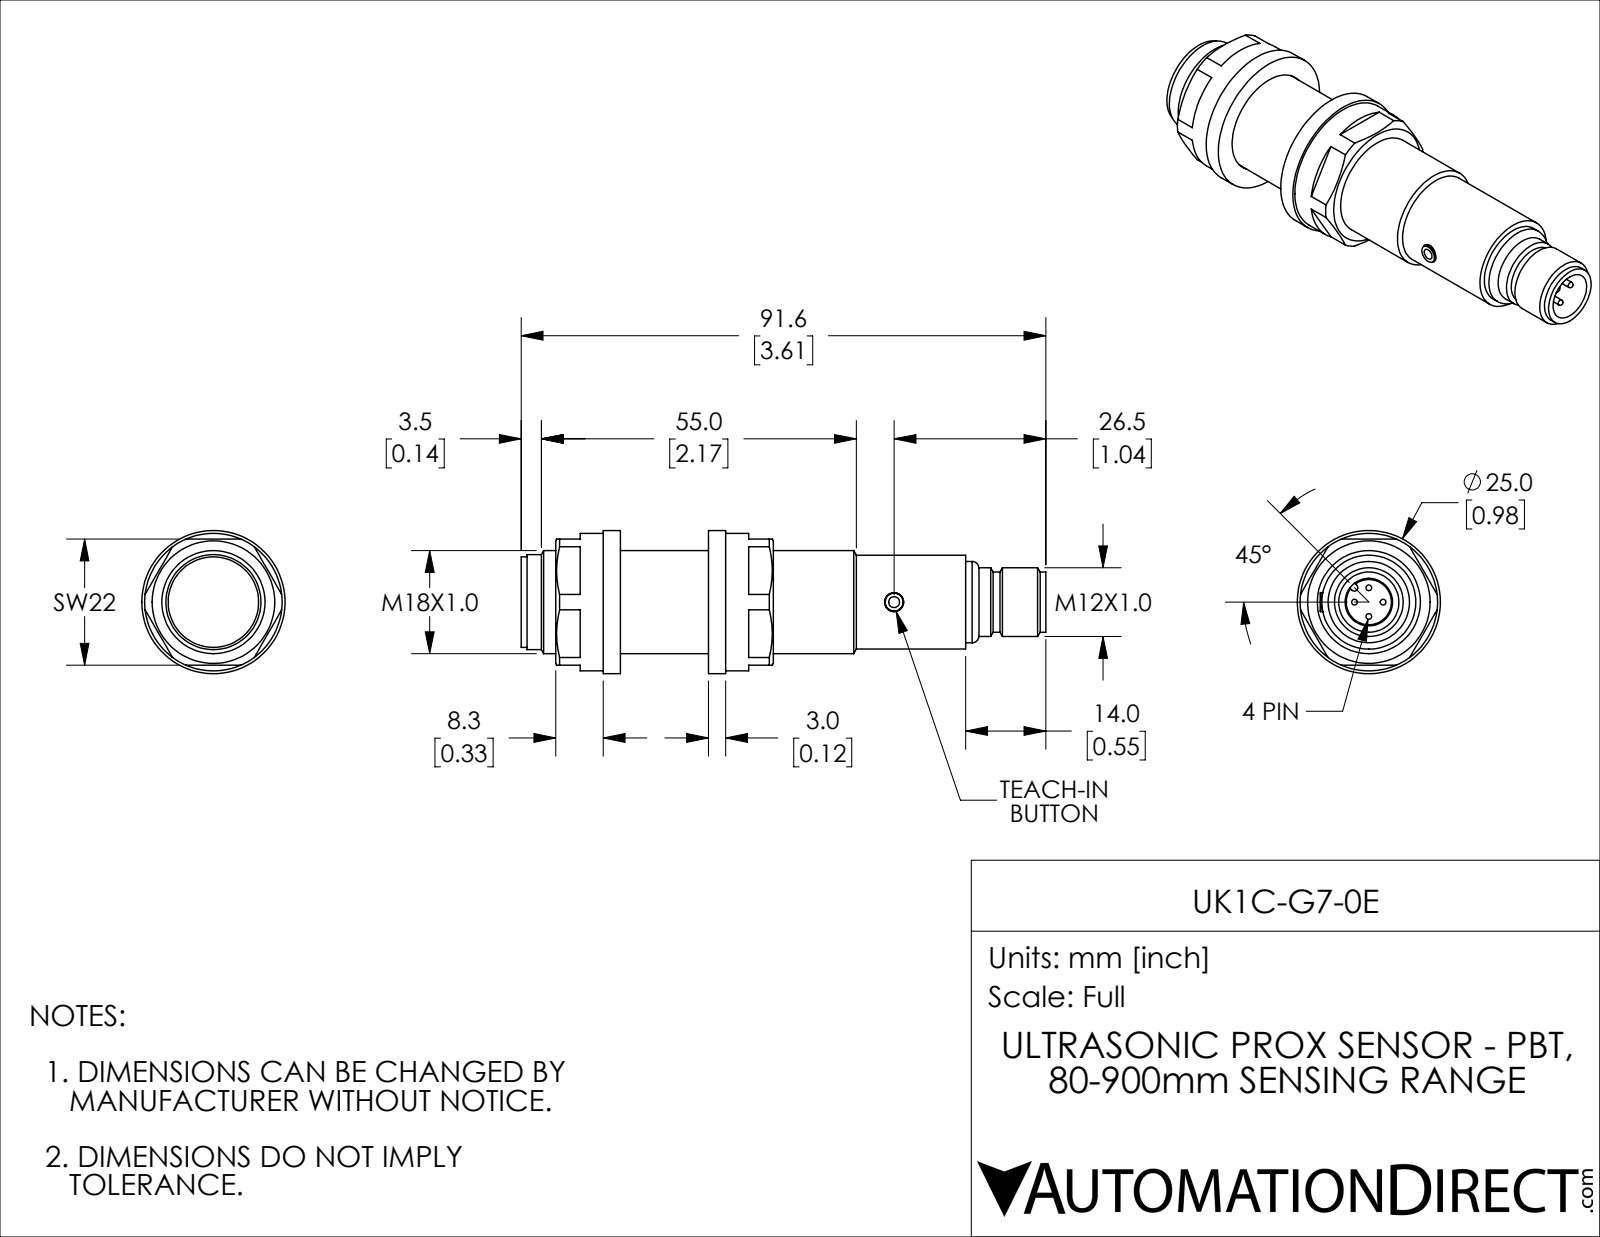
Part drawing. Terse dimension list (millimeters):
name: UK1C-G7-0E
written by: SolidWorks 2018 (AUTOMOTIVE_DESIGN)
unit: mm
bodies: 6 solids, 123 faces (43 planar, 49 cylindrical, 31 other)
size: 91.6 × 25 × 25
volume: 24 200 mm³; area: 10 330 mm²
holes: 1× ⌀3.3, 1× ⌀8.3, 1× ⌀18, 1× ⌀18.2
bosses: 4× ⌀1, 1× ⌀25, 1× ⌀24, 1× ⌀16.6, 1× ⌀16.4, 1× ⌀15.8, 1× ⌀14.2, 1× ⌀12
rounds: 1× R0.6
face distances: 3, 18.4, 21.4, 15.4, 22, 8.3, 11.3, 26.7, 29.7, 14.3
